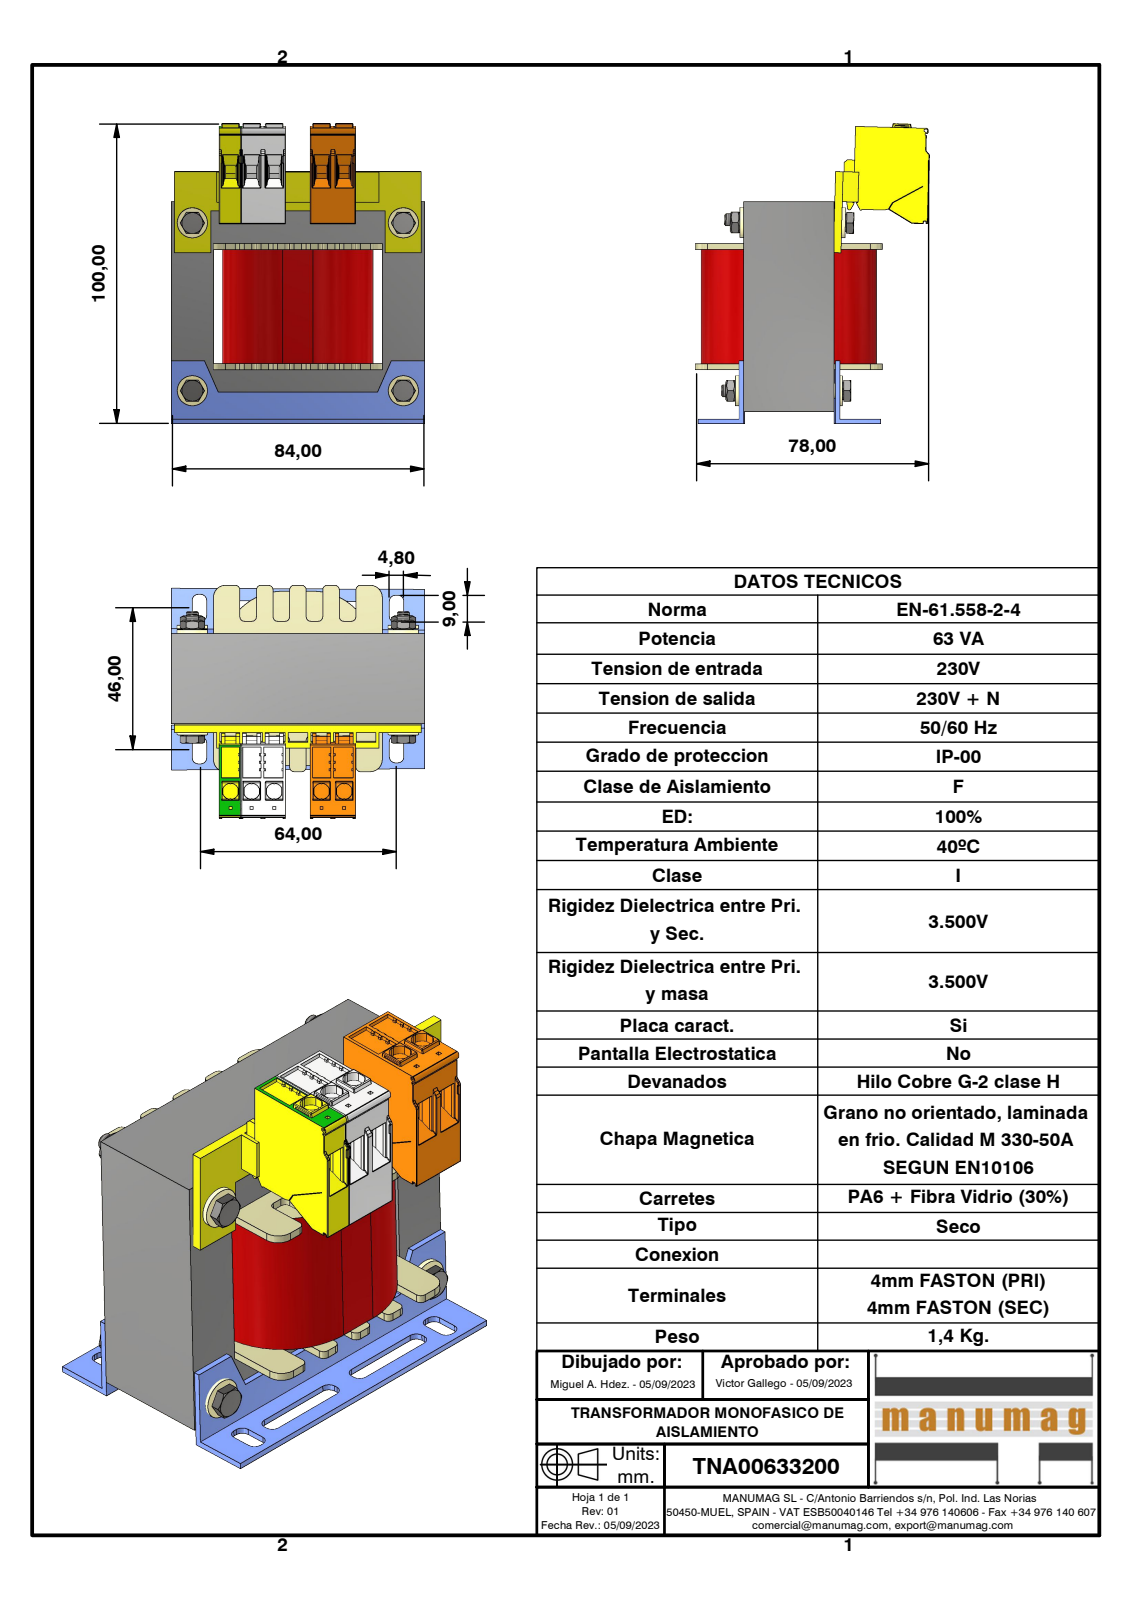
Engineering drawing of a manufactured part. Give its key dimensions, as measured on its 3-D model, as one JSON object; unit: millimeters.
{"part_name": "TNA00633200; EI84 x 70 - 30 (RC28); EI84; EI 84 X 70 - 30 (+7 more)", "step_written_by": "Autodesk Inventor 2023 (AUTOMOTIVE_DESIGN)", "units": "millimeters", "bodies": {"solids": 24, "faces": 5214, "planar": 4274, "cylindrical": 636, "other": 304}, "overall_size": [101.67, 84.08, 76.75], "volume_mm3": 247483, "surface_area_mm2": 82675, "round_holes": [[4, 8], [3.24, 4], [4.5, 4]], "round_bosses_or_shafts": [[10, 8], [4.9, 8], [5.9, 4], [3.62, 4], [4, 2]], "partial_cylinders_radius": [[0.15, 214], [1.5, 64], [0.2, 58], [2, 48], [0.5, 14], [4, 8], [0.3, 6], [5, 6]], "face_to_face_distances": [14, 28, 30.01, 56, 1.5, 14.01, 56.02, 2, 70, 42], "hole_center_spacings": [70, 89.64, 55.99, 56, 55.98, 56.01, 89.63, 89.65]}
